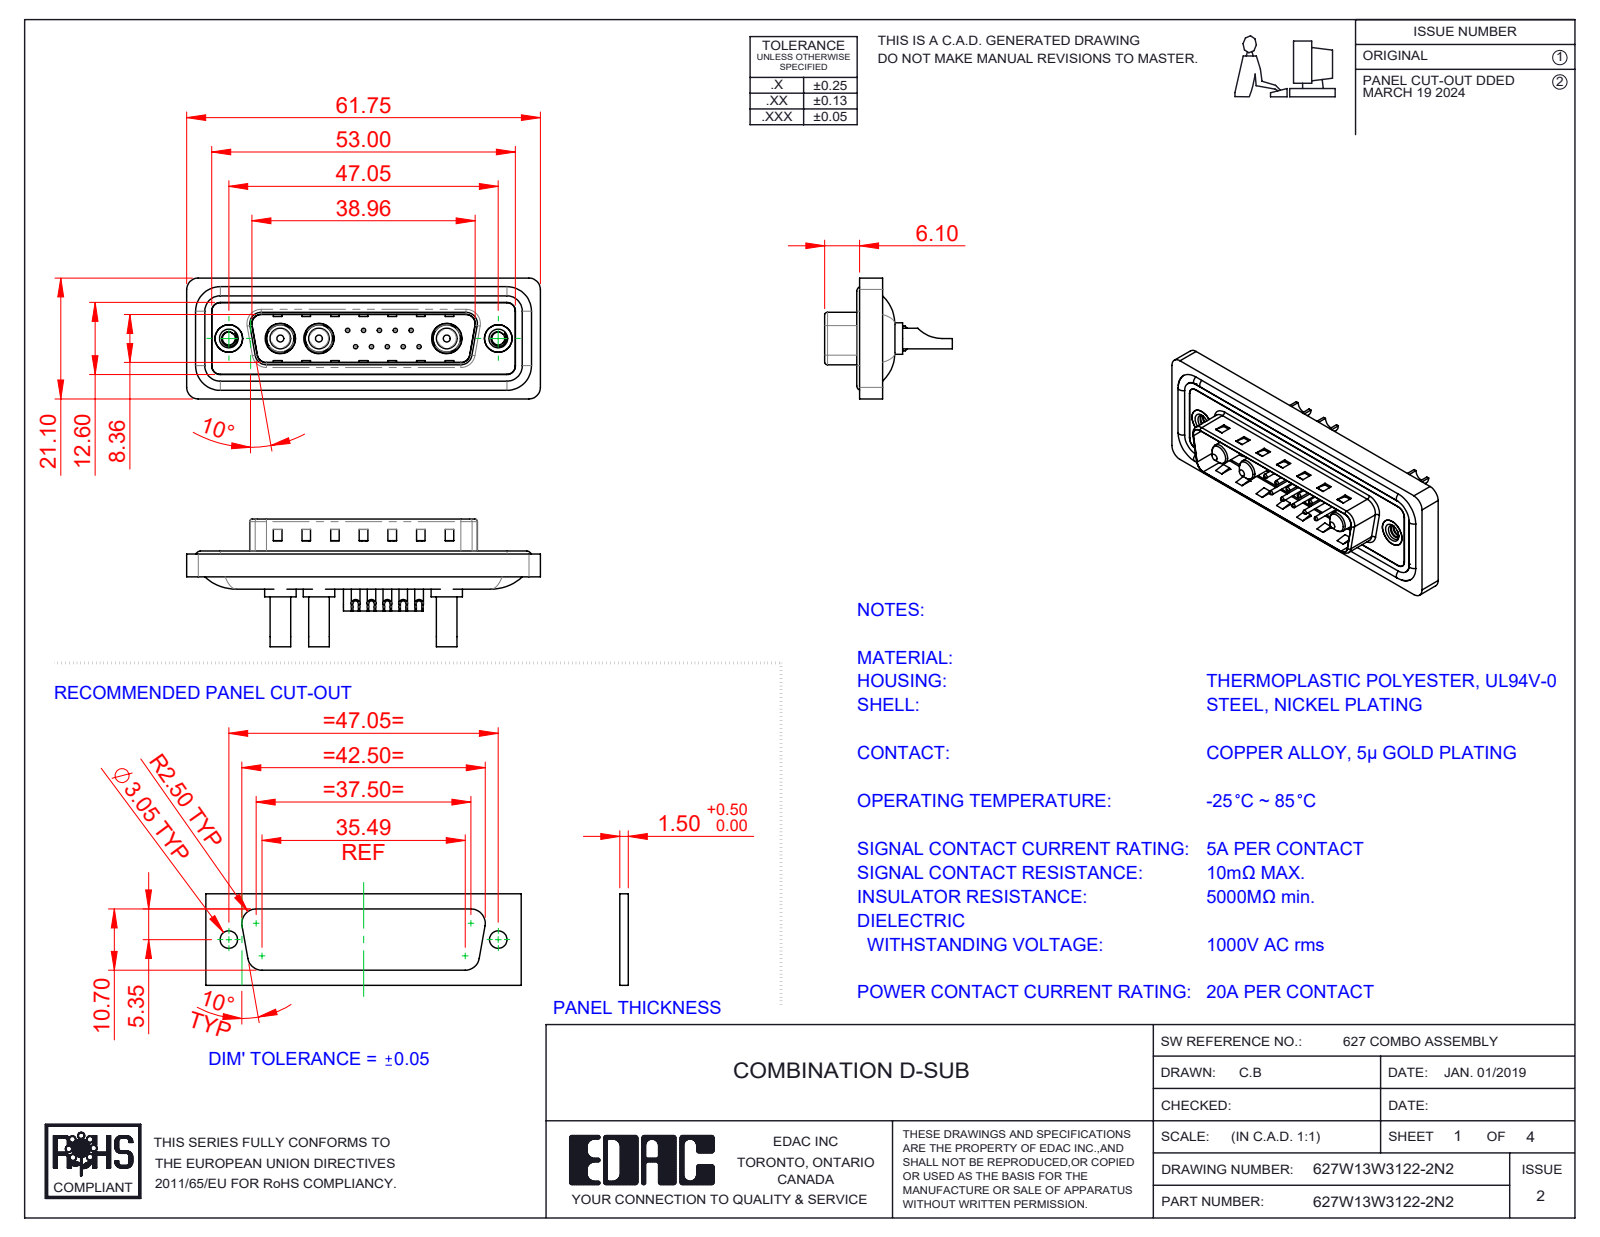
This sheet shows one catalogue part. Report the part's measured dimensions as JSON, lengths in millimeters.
{"part_name": "627Combo Threaded Rivet_2; 627Combo Waterproof Housing_25 Contacts; 627Combo Contact Row 1_22; 627Combo Shell Rear_25 Contacts (+5 more)", "step_written_by": "SolidWorks 2023 (CONFIG_CONTROL_DESIGN)", "units": "millimeters", "bodies": {"solids": 23, "faces": 988, "planar": 338, "cylindrical": 414, "other": 236}, "overall_size": [61.75, 22.3, 21.1], "volume_mm3": 7389, "surface_area_mm2": 12202, "round_holes": [[0.75, 10], [1, 10], [1.6, 10], [2, 10], [2.7, 3], [4.85, 3], [5.3, 3], [2.26, 2], [4, 2], [4.8, 2], [5, 2]], "round_bosses_or_shafts": [[1.5, 10], [1.6, 4], [5.5, 3], [5.2, 3], [4.75, 3], [3.75, 3], [3.6, 3], [4.9, 2]], "partial_cylinders_radius": [[1.5, 22], [2, 18], [0.5, 8], [1.6, 8], [1, 6], [0.25, 4], [0.6, 4], [0.65, 4]], "face_to_face_distances": [0.4, 1.5, 1.1, 1.6, 0.5, 3.1, 2.9, 0.82, 9.58, 4.1], "hole_center_spacings": [3.16, 2.77, 5.04, 5.54, 7.49, 5.03, 8.31, 10.11]}
